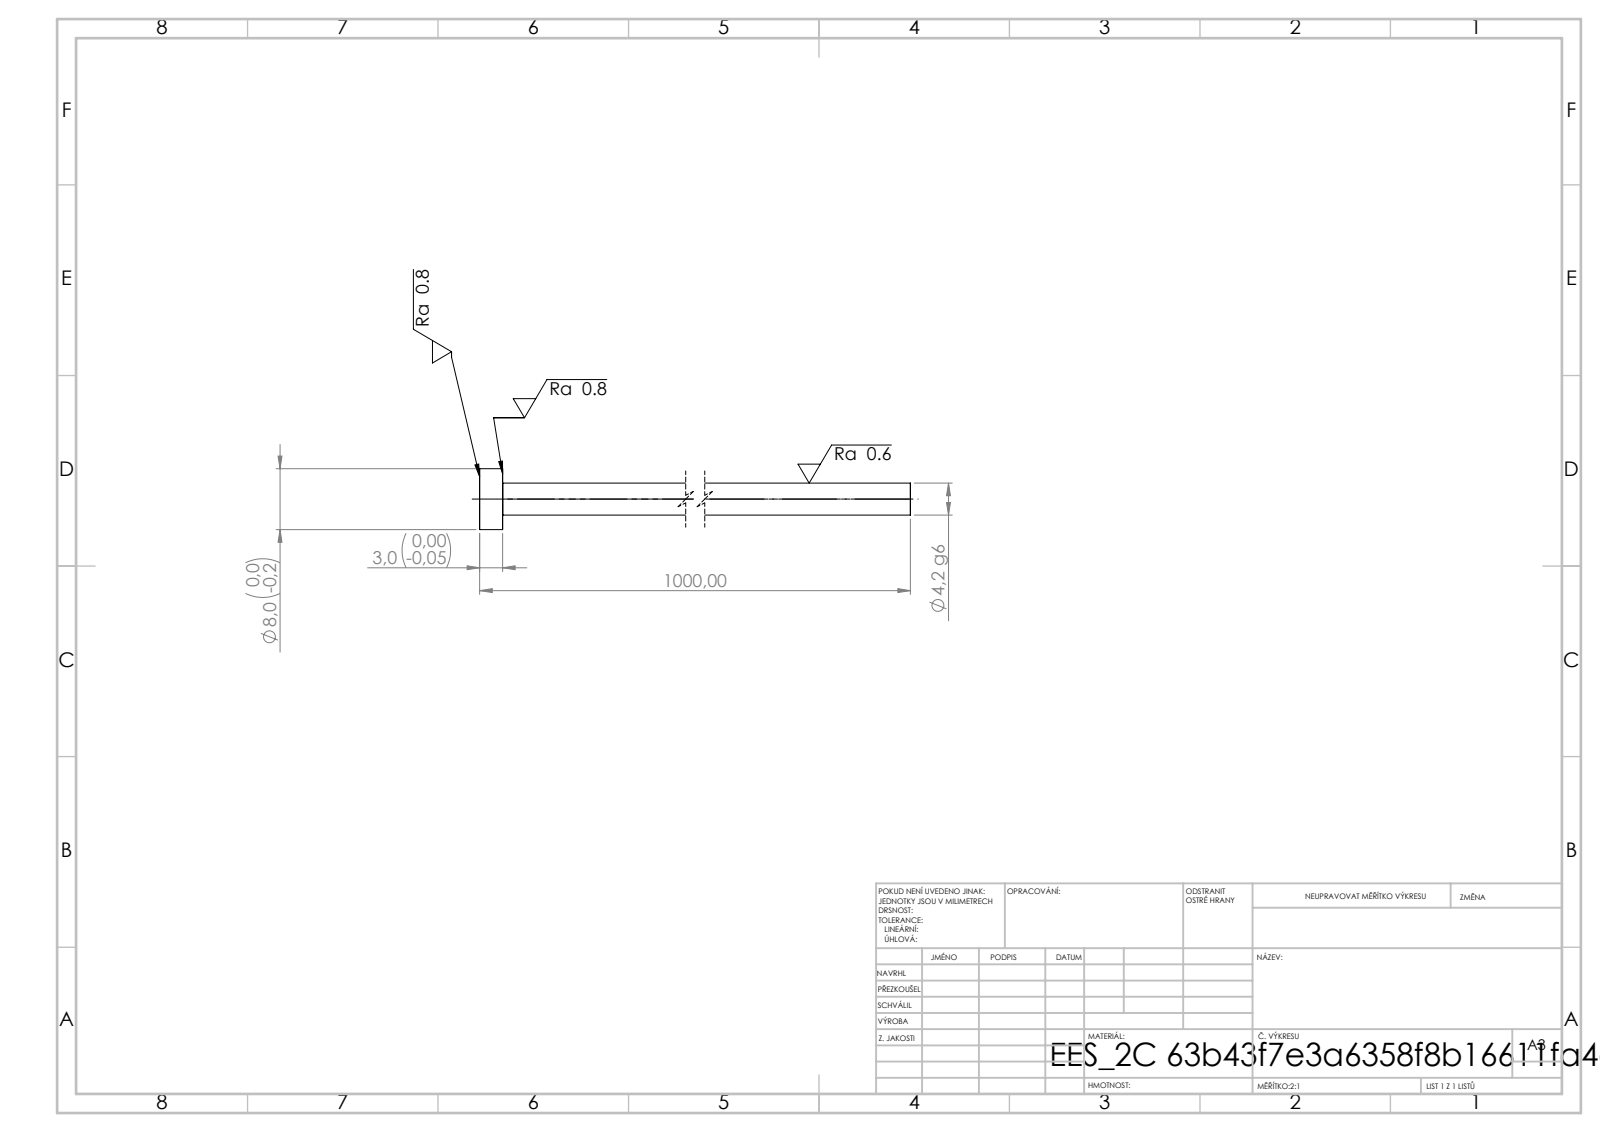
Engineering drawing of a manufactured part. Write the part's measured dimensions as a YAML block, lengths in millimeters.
step_written_by: "SolidWorks 2019 (CONFIG_CONTROL_DESIGN)"
units: millimeters
bodies: {solids: 1, faces: 7, planar: 3, cylindrical: 4, other: 0}
overall_size: [1000, 8, 8]
volume: 13964
surface_area: 13331
round_bosses_or_shafts:
  - {diameter: 8, count: 1}
  - {diameter: 4.2, count: 1}
face_to_face_distances: [3, 1000, 997]
